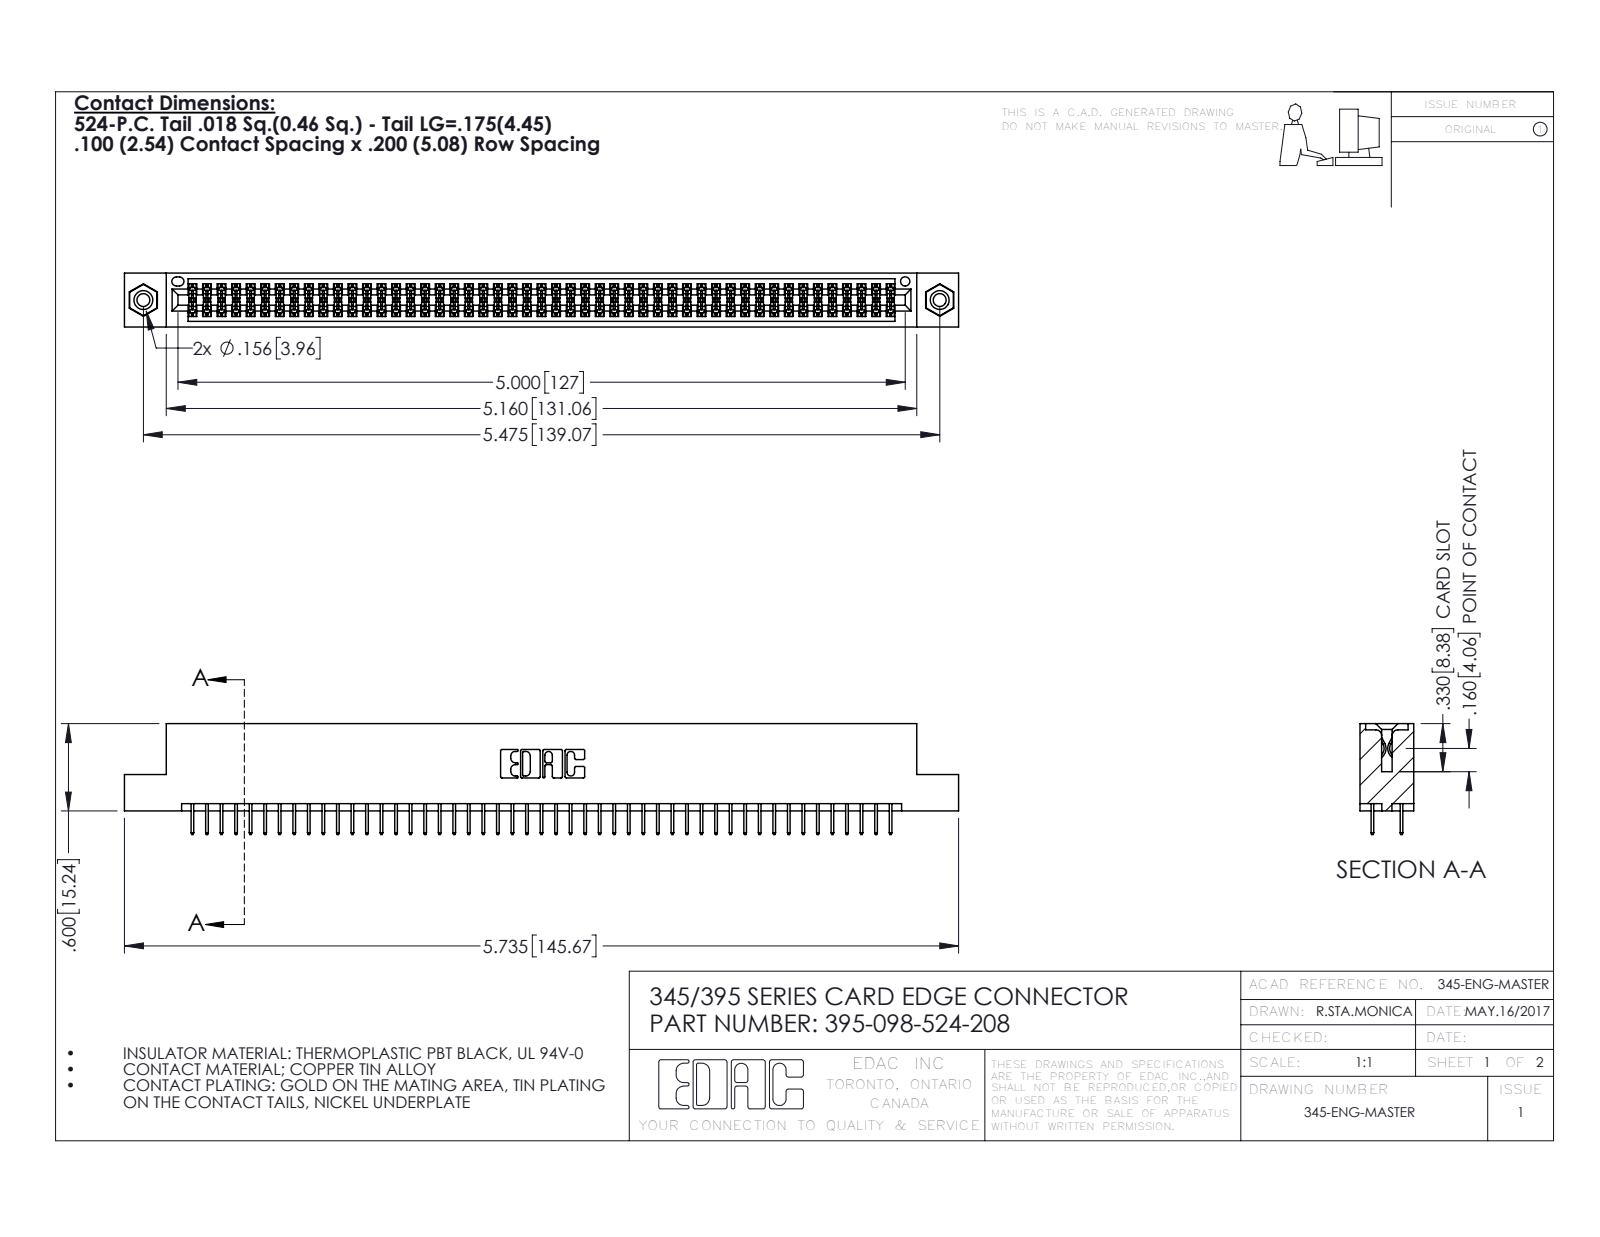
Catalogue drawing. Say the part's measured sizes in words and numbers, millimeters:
The part is named "395-098-524-208; 345-292-001_345-293-124; 345 Part_Flush Mounting Lugs - 0.156 Dia-TI; 345-250-001_345-250-003-102". Its 3-D file was written by "SolidWorks 2016 (CONFIG_CONTROL_DESIGN)". It is 101 solids with 5478 faces: 3934 planar, 1528 cylindrical and 16 other. Overall it measures 145.7 by 19.4 by 9.4 millimeters. Its volume is 14 100 cubic millimeters and its surface area 20 540 square millimeters. Round holes: 2 of diameter 2.3, 2 of diameter 3.2, 2 of diameter 4, 1 of diameter 1.6. Round bosses or shafts: 2 of diameter 3.9. Partial cylindrical surfaces (rounded edges, fillets, slot ends): 147 of radius 0.2, 22 of radius 0.3, 6 of radius 0.2, 6 of radius 0.8, 3 of radius 0.7, 2 of radius 0.4, 2 of radius 0.5, 2 of radius 0.6. The main face-to-face distances are 1.8, 7.6, 5.1, 9.4, 2.5, 6.9, 0.6, 5.7, 1.8, 4.4. The hole center spacings are 6.9, 133.1, 139.1.
